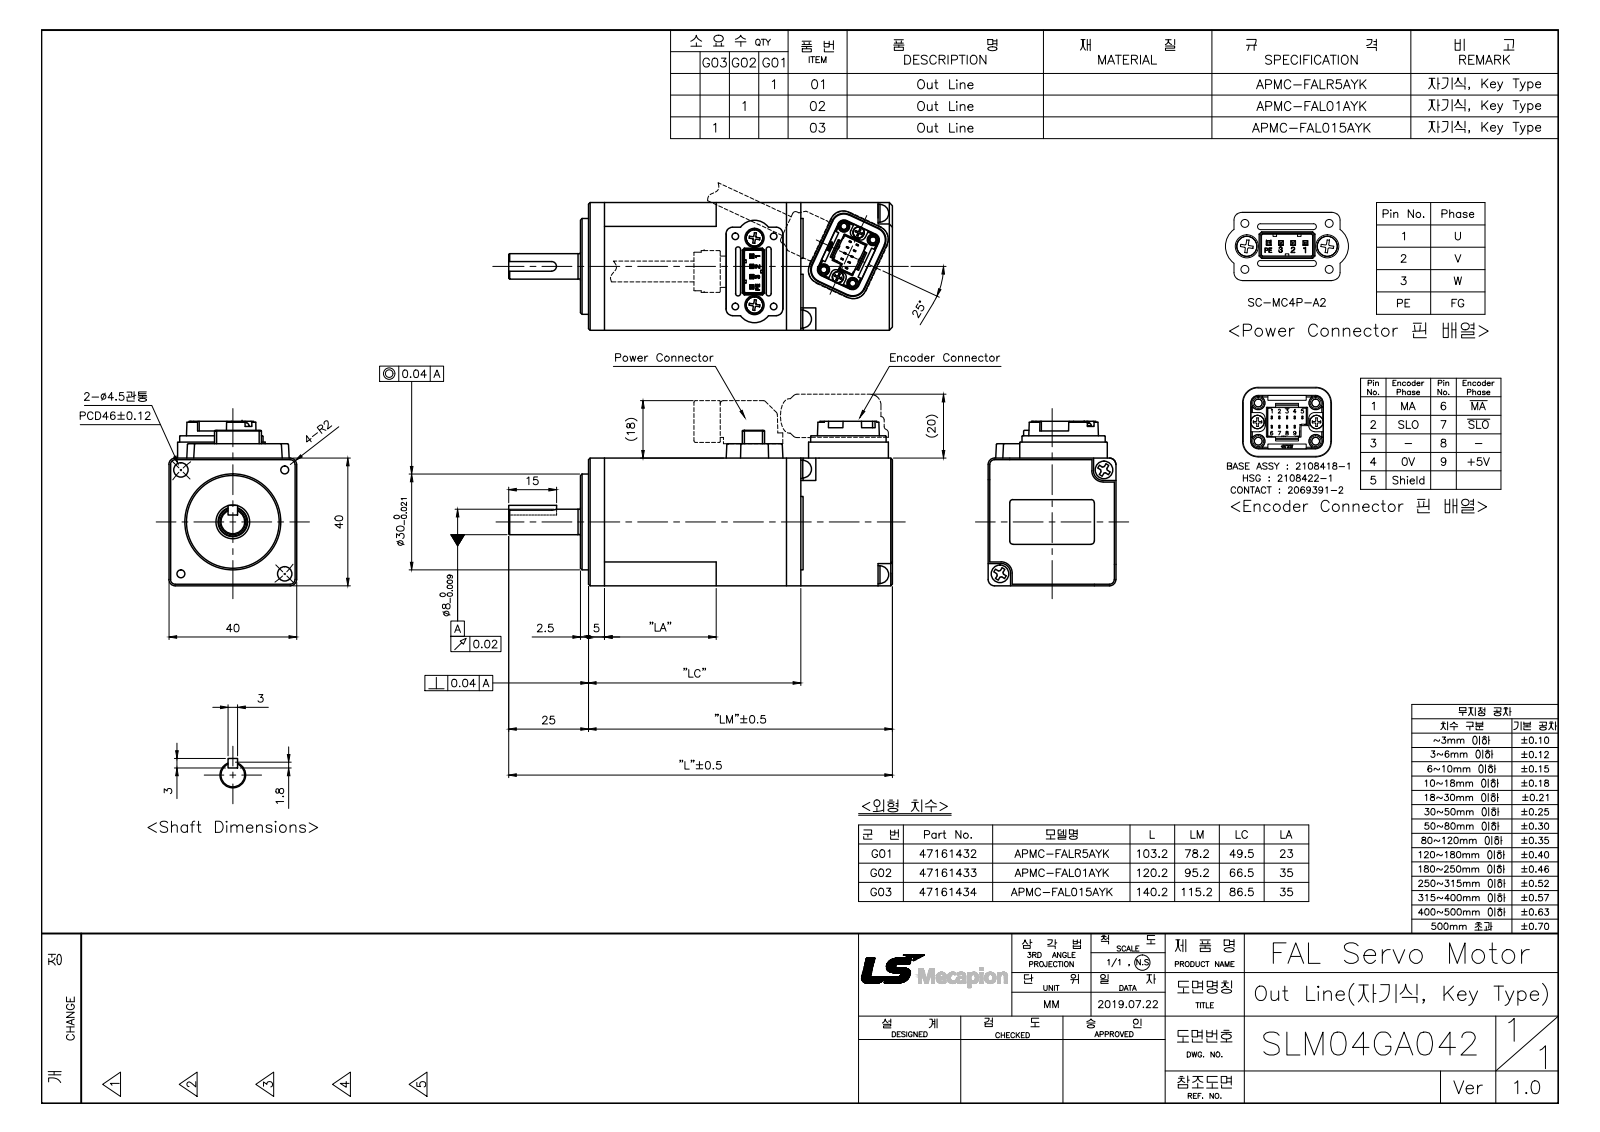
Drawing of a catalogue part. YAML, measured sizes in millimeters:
part_name: "APMC-FALR5AM8K"
step_written_by: "SolidWorks 2011 (AUTOMOTIVE_DESIGN)"
units: millimeters
bodies: {solids: 29, faces: 1372, planar: 914, cylindrical: 291, other: 167}
overall_size: [103.2, 51.5, 40]
volume: 129719
surface_area: 39538
round_holes:
  - {diameter: 2.1, count: 10}
  - {diameter: 3, count: 6}
  - {diameter: 3.6, count: 4}
  - {diameter: 2, count: 2}
  - {diameter: 2.2, count: 2}
  - {diameter: 2.5, count: 2}
  - {diameter: 4.5, count: 2}
  - {diameter: 6, count: 2}
  - {diameter: 3.3, count: 1}
  - {diameter: 3.4, count: 1}
  - {diameter: 10.6, count: 1}
round_bosses_or_shafts:
  - {diameter: 5.4, count: 6}
  - {diameter: 30, count: 1}
  - {diameter: 9.8, count: 1}
  - {diameter: 8, count: 1}
partial_cylinders:
  - {radius: 0.2, count: 20}
  - {radius: 0.15, count: 9}
  - {radius: 1, count: 8}
  - {radius: 0.45, count: 7}
  - {radius: 1.5, count: 7}
  - {radius: 0.11, count: 6}
  - {radius: 0.3, count: 4}
  - {radius: 0.76, count: 4}
face_to_face_distances: [40, 4.5, 44.5, 0.7, 5.2, 45.2, 5, 45, 28, 28.7]
hole_center_spacings: [6.02, 16, 22.32, 23, 32.52, 5, 5.01, 10]
